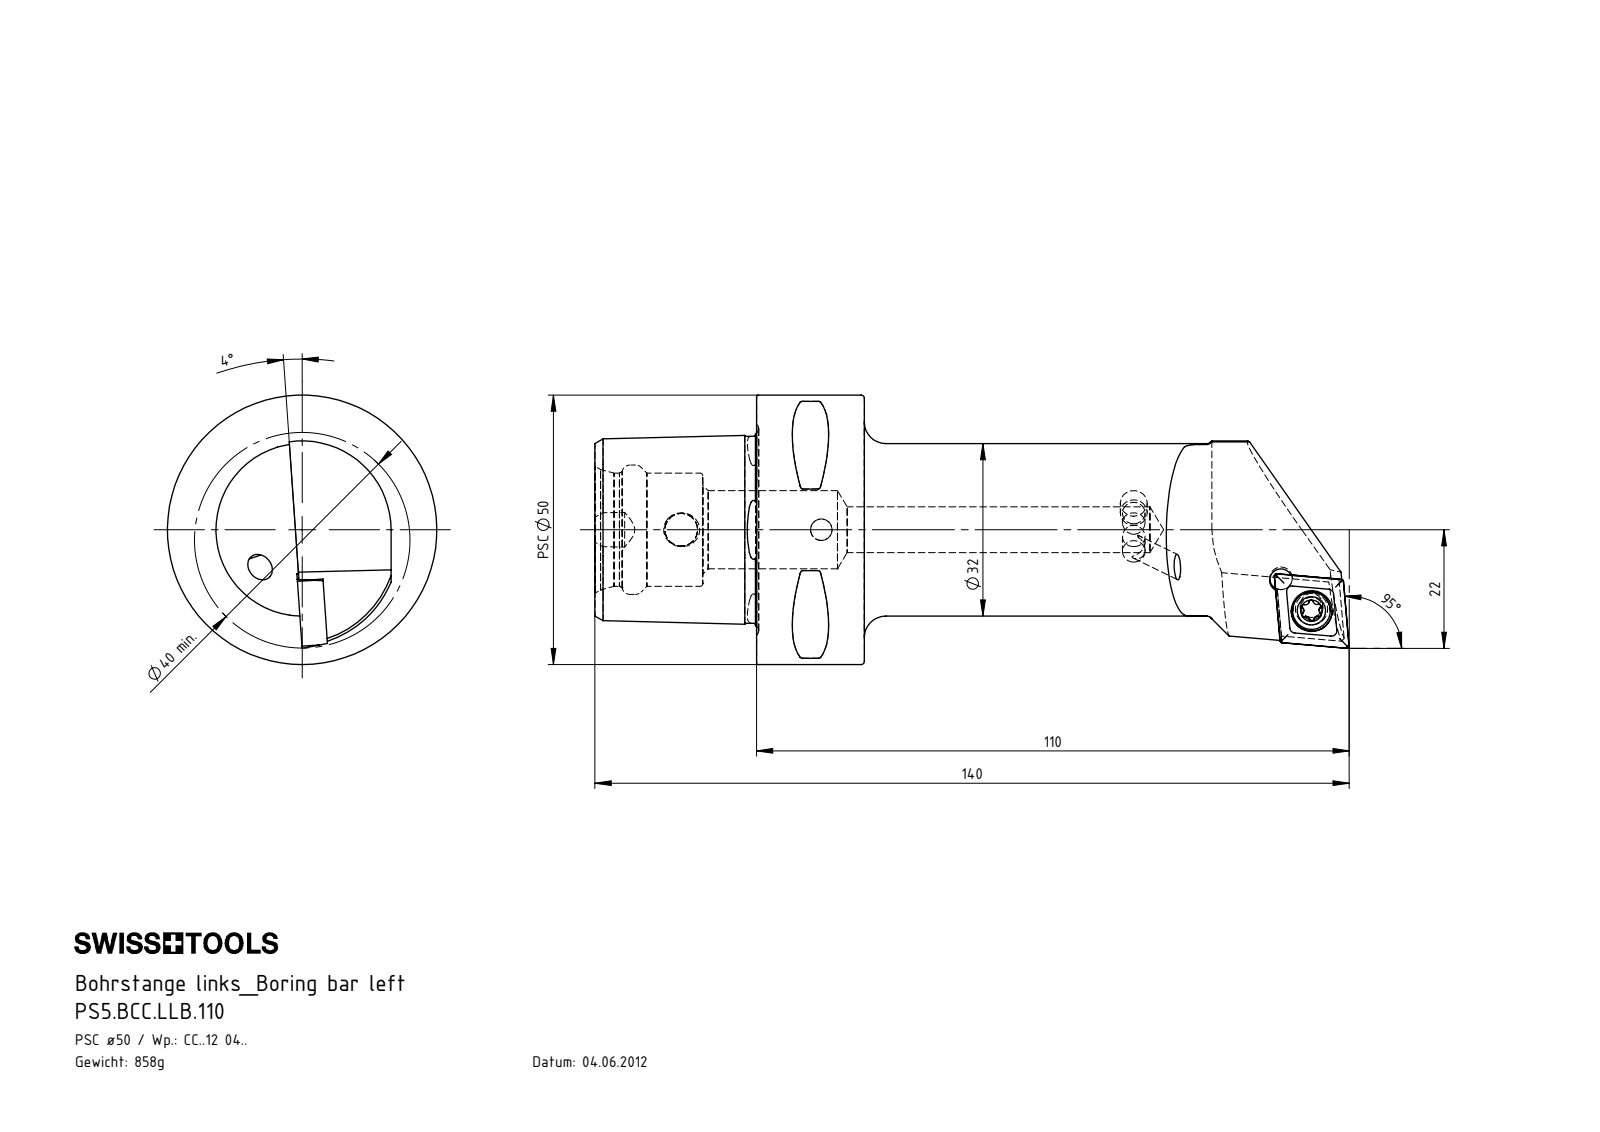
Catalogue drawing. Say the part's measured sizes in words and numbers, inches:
The part is named "CCMT120404; KVT_MB_600_050; PS5-BCC.LLB.110_A; PS5.BCC.LLB.110 (+1 more)". Its 3-D file was written by "SolidWorks 2017 (AUTOMOTIVE_DESIGN)". It is 5 solids with 281 faces: 49 planar, 74 cylindrical and 158 other. Overall it measures 5.512 by 1.969 by 1.969 inches. Its volume is 6.673 cubic inches and its surface area 37.07 square inches. Round holes: 4 of diameter 0.165, 2 of diameter 0.157, 1 of diameter 0.217, 1 of diameter 0.24, 1 of diameter 0.299, 1 of diameter 0.335, 1 of diameter 0.571, 1 of diameter 0.827, 1 of diameter 0.945. Round bosses or shafts: 2 of diameter 0.197, 1 of diameter 1.969, 1 of diameter 1.26, 1 of diameter 0.276. Partial cylindrical surfaces (rounded edges, fillets, slot ends): 8 of radius 0.02, 6 of radius 0.015, 3 of radius 0.027, 3 of radius 0.027, 1 of radius 0.118, 1 of radius 0.157, 1 of radius 0.65, 1 of radius 0.748. The main face-to-face distances are 0.787, 1.181, 1.969, 0.176, 0.755, 1.748, 0.394, 1.173, 0.386, 0.795. The hole center spacings are 0.315, 0.319, 1.024.
